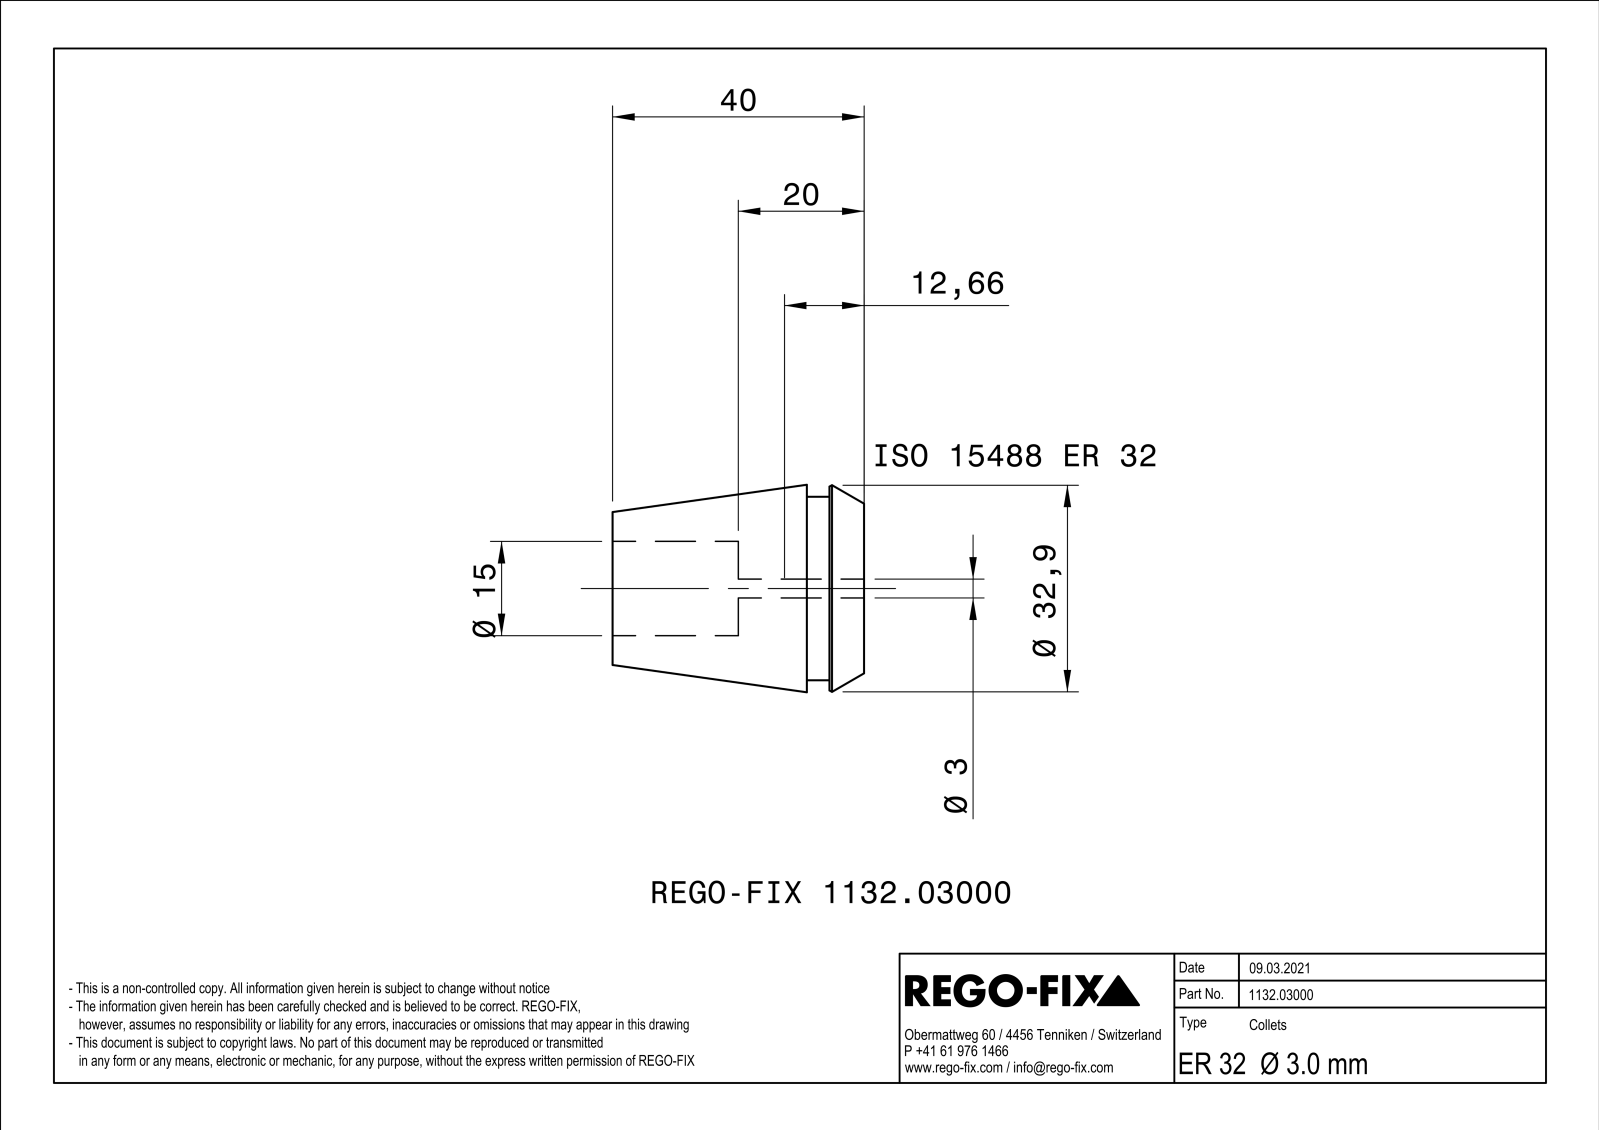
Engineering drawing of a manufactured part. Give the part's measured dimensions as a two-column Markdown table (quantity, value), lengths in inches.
| quantity | value |
| --- | --- |
| part name | NOCUT |
| STEP written by | SIEMENS PLM Software Solid Edge ST10 (AUTOMOTIVE_DESIGN) |
| units | inches |
| bodies | 1 solid, 256 faces (88 planar, 48 cylindrical, 120 other) |
| overall size | 1.575 × 1.299 × 1.299 |
| volume | 1.214 in³ |
| surface area | 23.22 in² |
| round holes (diameter × count) | 0.591 × 1 |
| round bosses / shafts (diameter × count) | 1.15 × 1 |
| partial cylindrical surfaces (radius × count) | 0.012 × 13, 0.059 × 1 |
| main face-to-face distances | 0.024, 0.024, 0.023, 1.575, 0.787, 0.358, 1.217, 0.217, 0.142, 1.358 |
